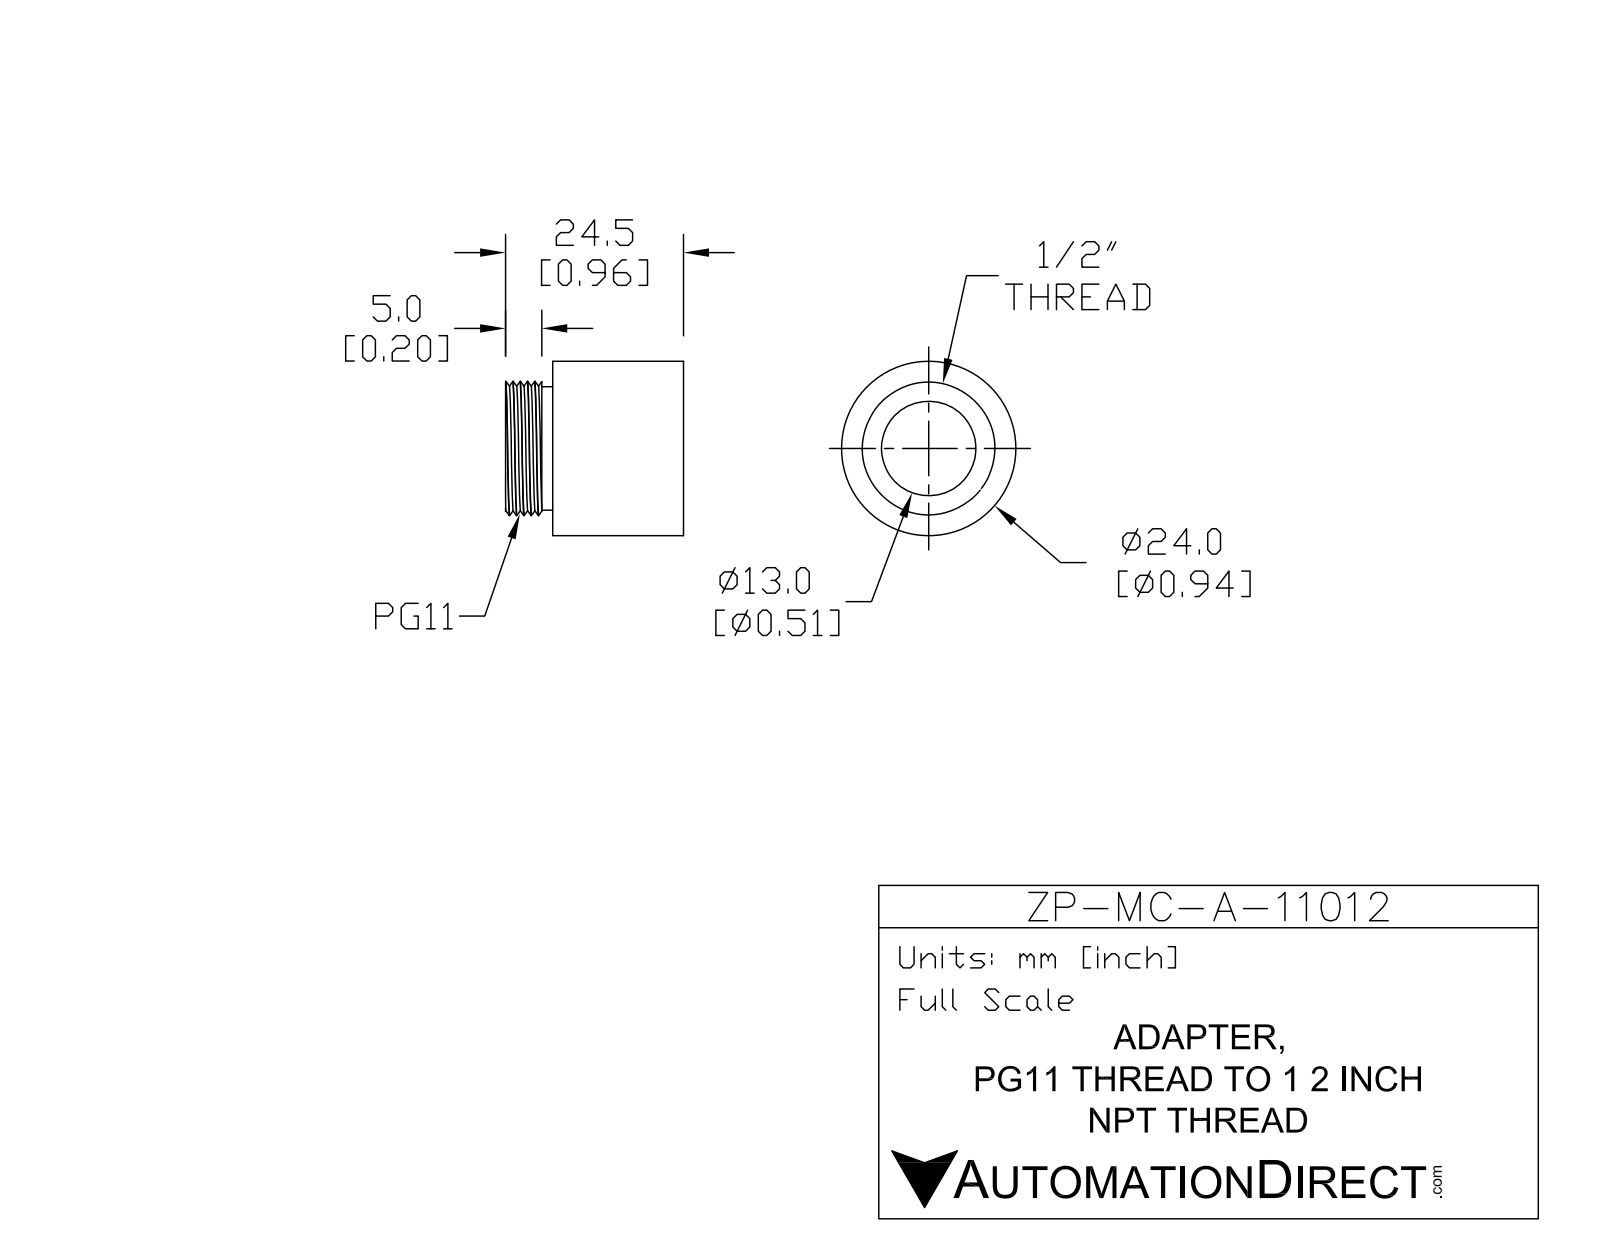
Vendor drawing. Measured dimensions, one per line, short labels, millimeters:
name: ZP-MC-A-11012
written by: SolidWorks 2011 (AUTOMOTIVE_DESIGN)
unit: mm
bodies: 1 solid, 31 faces (6 planar, 20 cylindrical, 5 other)
size: 24.5 × 24 × 24
volume: 4 347 mm³; area: 4 523 mm²
holes: 1× ⌀13, 1× ⌀18.25
bosses: 1× ⌀24, 1× ⌀18.46, 1× ⌀17
face distances: 18, 2.74, 15.26, 6.5, 9.24, 24.5, 5, 1.5, 4.24, 19.5
